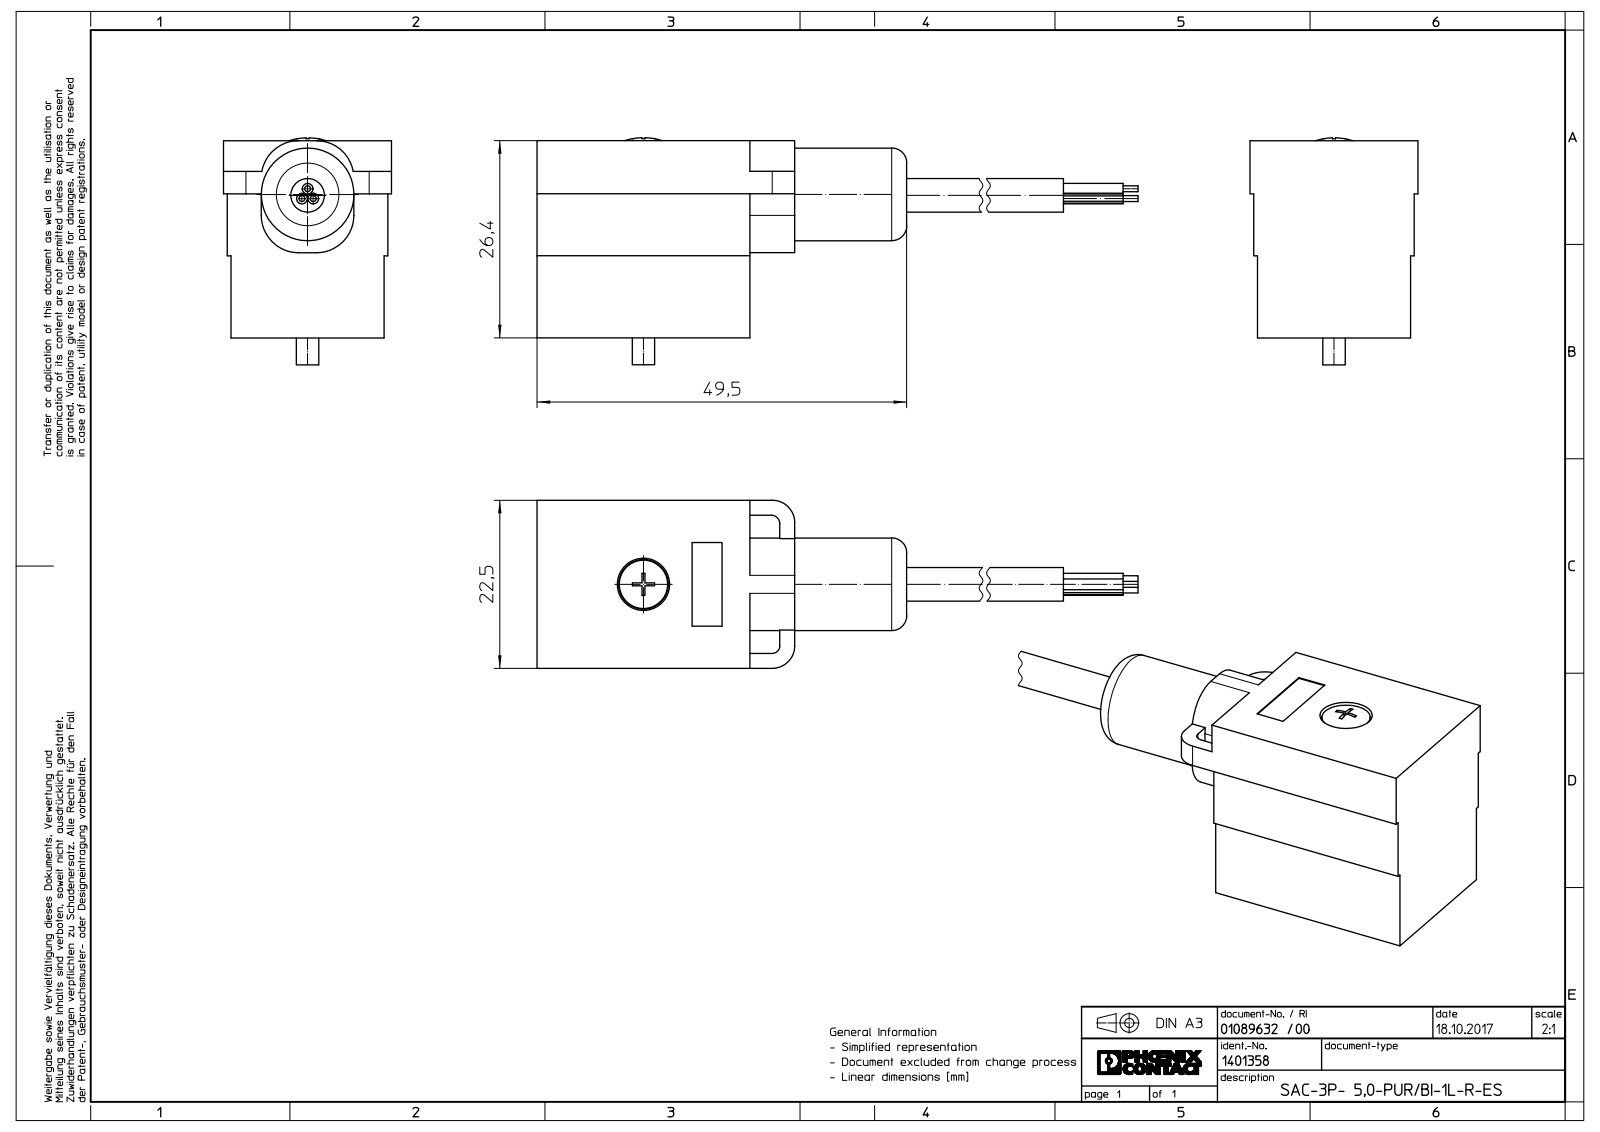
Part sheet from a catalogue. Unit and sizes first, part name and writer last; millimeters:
Units: millimetres
Overall size (bounding box): 159.5 × 30.39 × 22.5
Round holes (diameter × count): ⌀6.1 ×1, ⌀7 ×1
Round bosses / shafts (diameter × count): ⌀0.8 ×3, ⌀1.43 ×2, ⌀12.4 ×1, ⌀4.5 ×1, ⌀3 ×1
Partial cylindrical surfaces — rounded edges, fillets, slot ends (radius × count): R5 ×4, R3 ×2, R0.71 ×1, R1 ×1, R1.16 ×1
Main face-to-face distances: 0.5, 21.5, 21, 1, 22, 28.5, 24.9, 20.5, 22.5, 1.5
Volume: 19 763 mm³ · Surface area: 6 966 mm²
Bodies: 1 solid, 132 faces (93 planar, 33 cylindrical, 6 other)
Part name (STEP PRODUCT): 5813-1 Actuator cable - SAC-3P- 5,0-PURBI-1L-R-ES - 1401358; 5813 Actuator cable - SAC-3P- 5,0-PURBI-1L-R-ES - 1401358
STEP written by: Alibre (AUTOMOTIVE_DESIGN)
